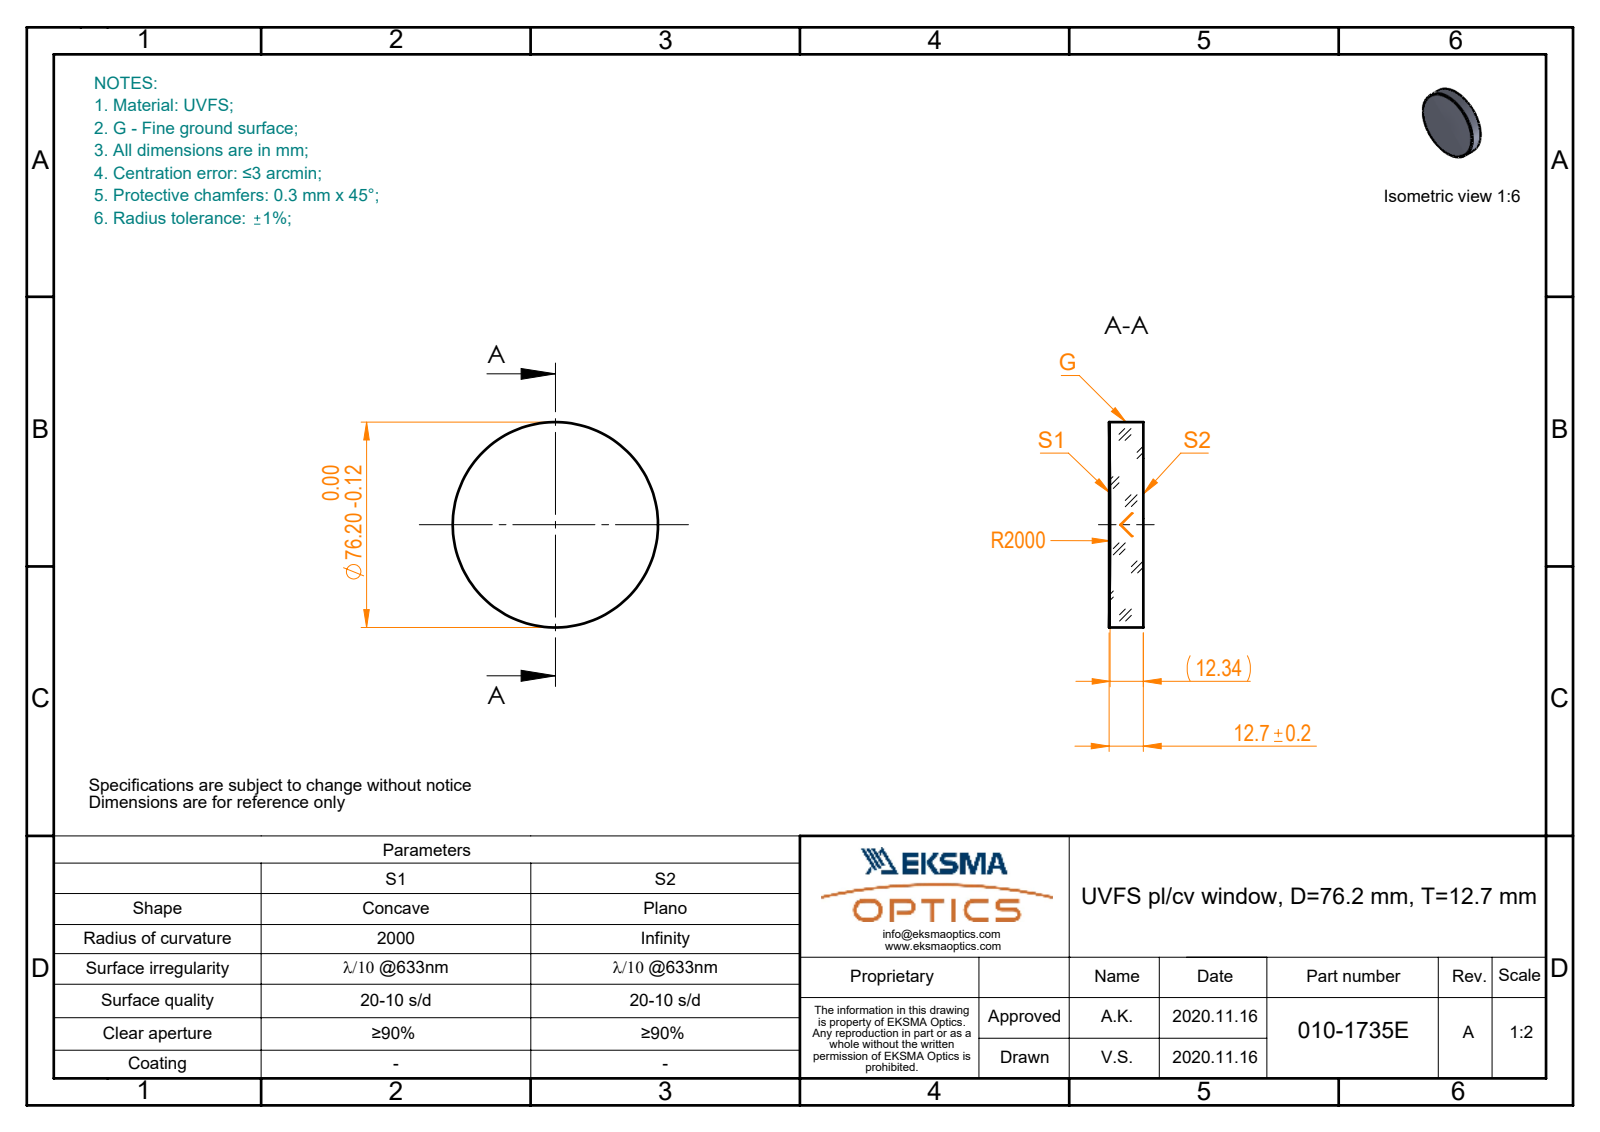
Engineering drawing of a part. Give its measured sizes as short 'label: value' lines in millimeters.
name: 010-1735E_UVFS_PCV_window
written by: SolidWorks 2019 (CONFIG_CONTROL_DESIGN)
unit: mm
bodies: 1 solid, 5 faces (1 planar, 2 cylindrical, 2 other)
size: 76.2 × 76.2 × 12.7
volume: 57 089 mm³; area: 12 161 mm²
bosses: 1× ⌀76.2
